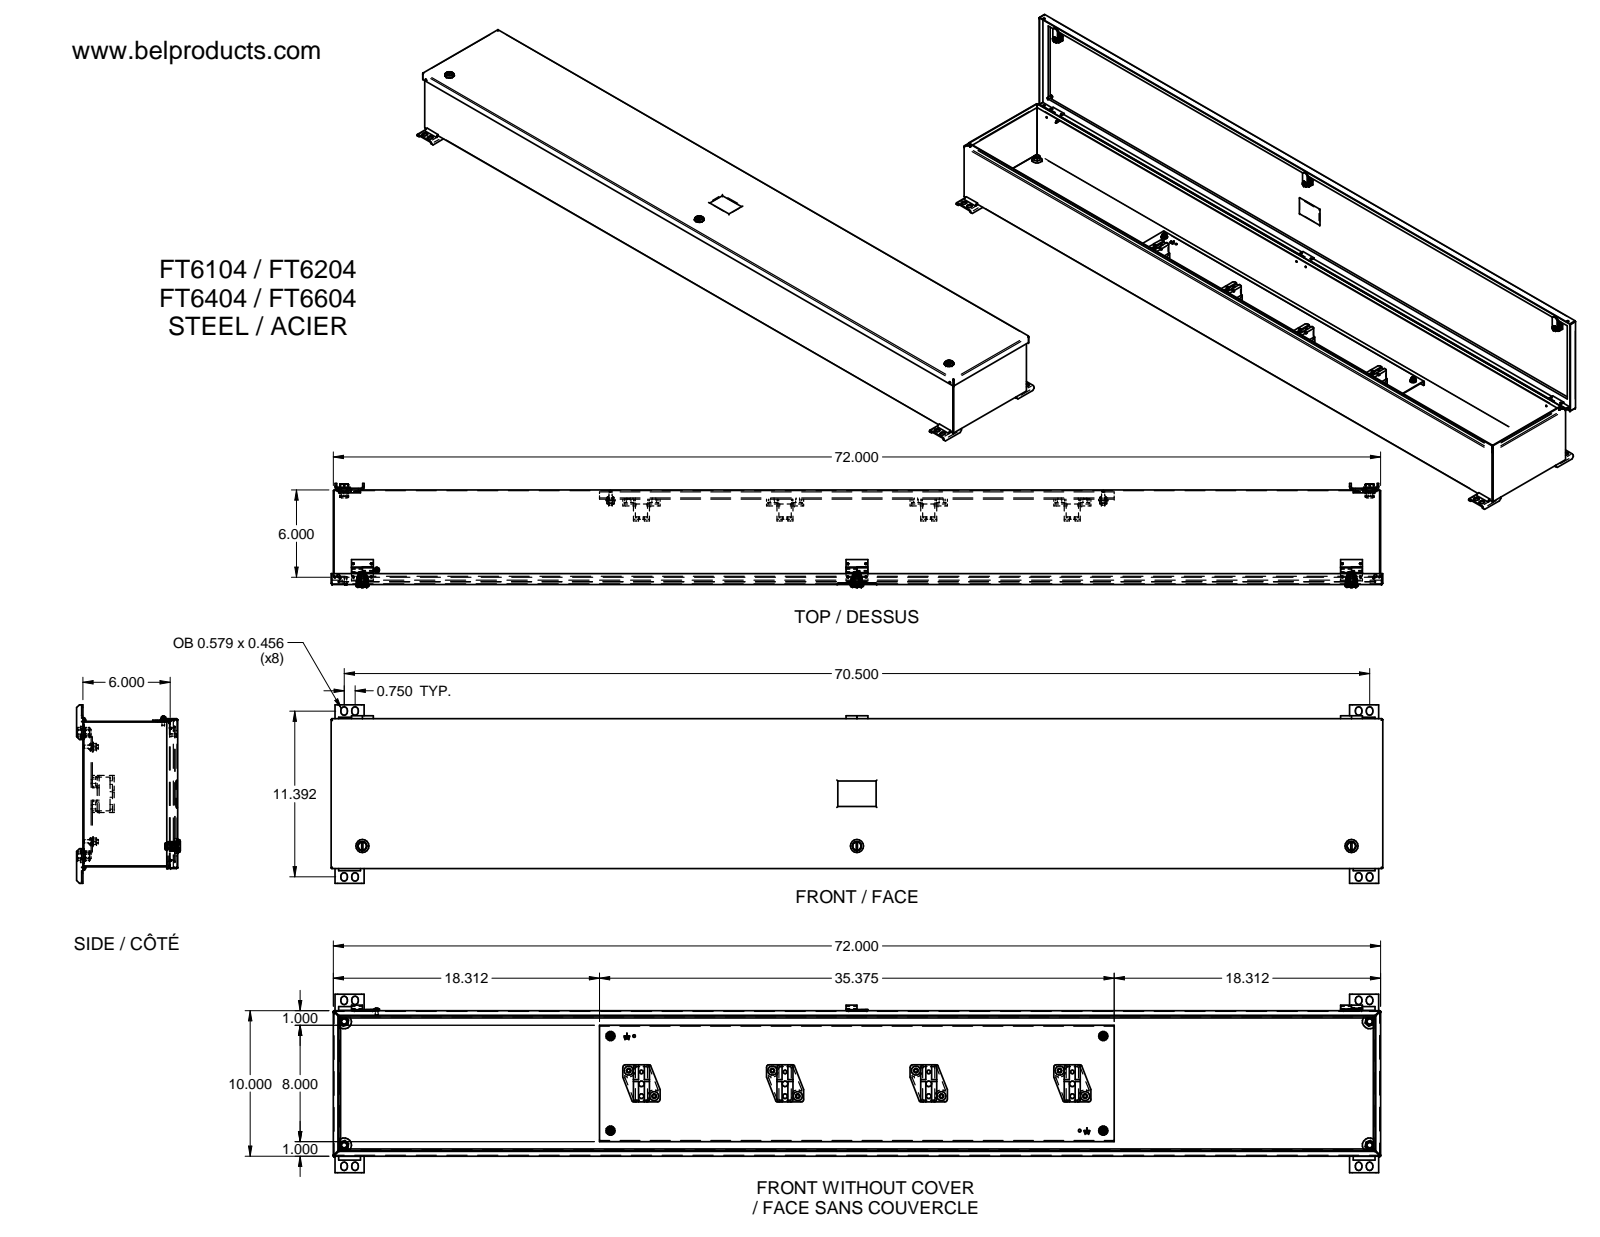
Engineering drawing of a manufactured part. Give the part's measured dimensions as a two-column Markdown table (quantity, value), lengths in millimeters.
| quantity | value |
| --- | --- |
| part name | LOCK AVEC TOURNEVIS TYPE 4-12 SANS CAME-oa8; HOSING-oa0; INSERT POUR TOURNEVIS-oa1; NOIX DE FIXATION-oa2 (+8 more) |
| STEP written by | Unknown (AUTOMOTIVE_DESIGN) |
| units | millimeters |
| bodies | 82 solids, 3005 faces (1746 planar, 606 cylindrical, 653 other) |
| overall size | 1836.42 × 311.56 × 180.97 |
| volume | 3 731 000 mm³ |
| surface area | 4 237 000 mm² |
| round holes (diameter × count) | 3.16 × 12, 3.3 × 12, 5.99 × 8, 6.35 × 8, 7.92 × 8, 9.53 × 8, 11.58 × 8, 15.88 × 8, 3.17 × 5, 7.14 × 4, 8.23 × 4, 9.02 × 4 |
| round bosses / shafts (diameter × count) | 3.17 × 12, 3.02 × 5, 20.62 × 4, 15.88 × 4, 5.56 × 4, 0.79 × 4, 22.86 × 3, 22.61 × 3 |
| partial cylindrical surfaces (radius × count) | 9.53 × 32, 4.76 × 28, 0.25 × 24, 0.81 × 16, 1.46 × 16, 5.79 × 16, 2.34 × 14, 1.52 × 8 |
| main face-to-face distances | 1.52, 252.48, 1.53, 163.93, 165.46, 162.41, 163.94, 250.96, 254, 1.91 |
| hole center spacings | 250.82, 501.65, 250.83, 863.6, 23.03, 62.86, 31.75, 211.1 |
